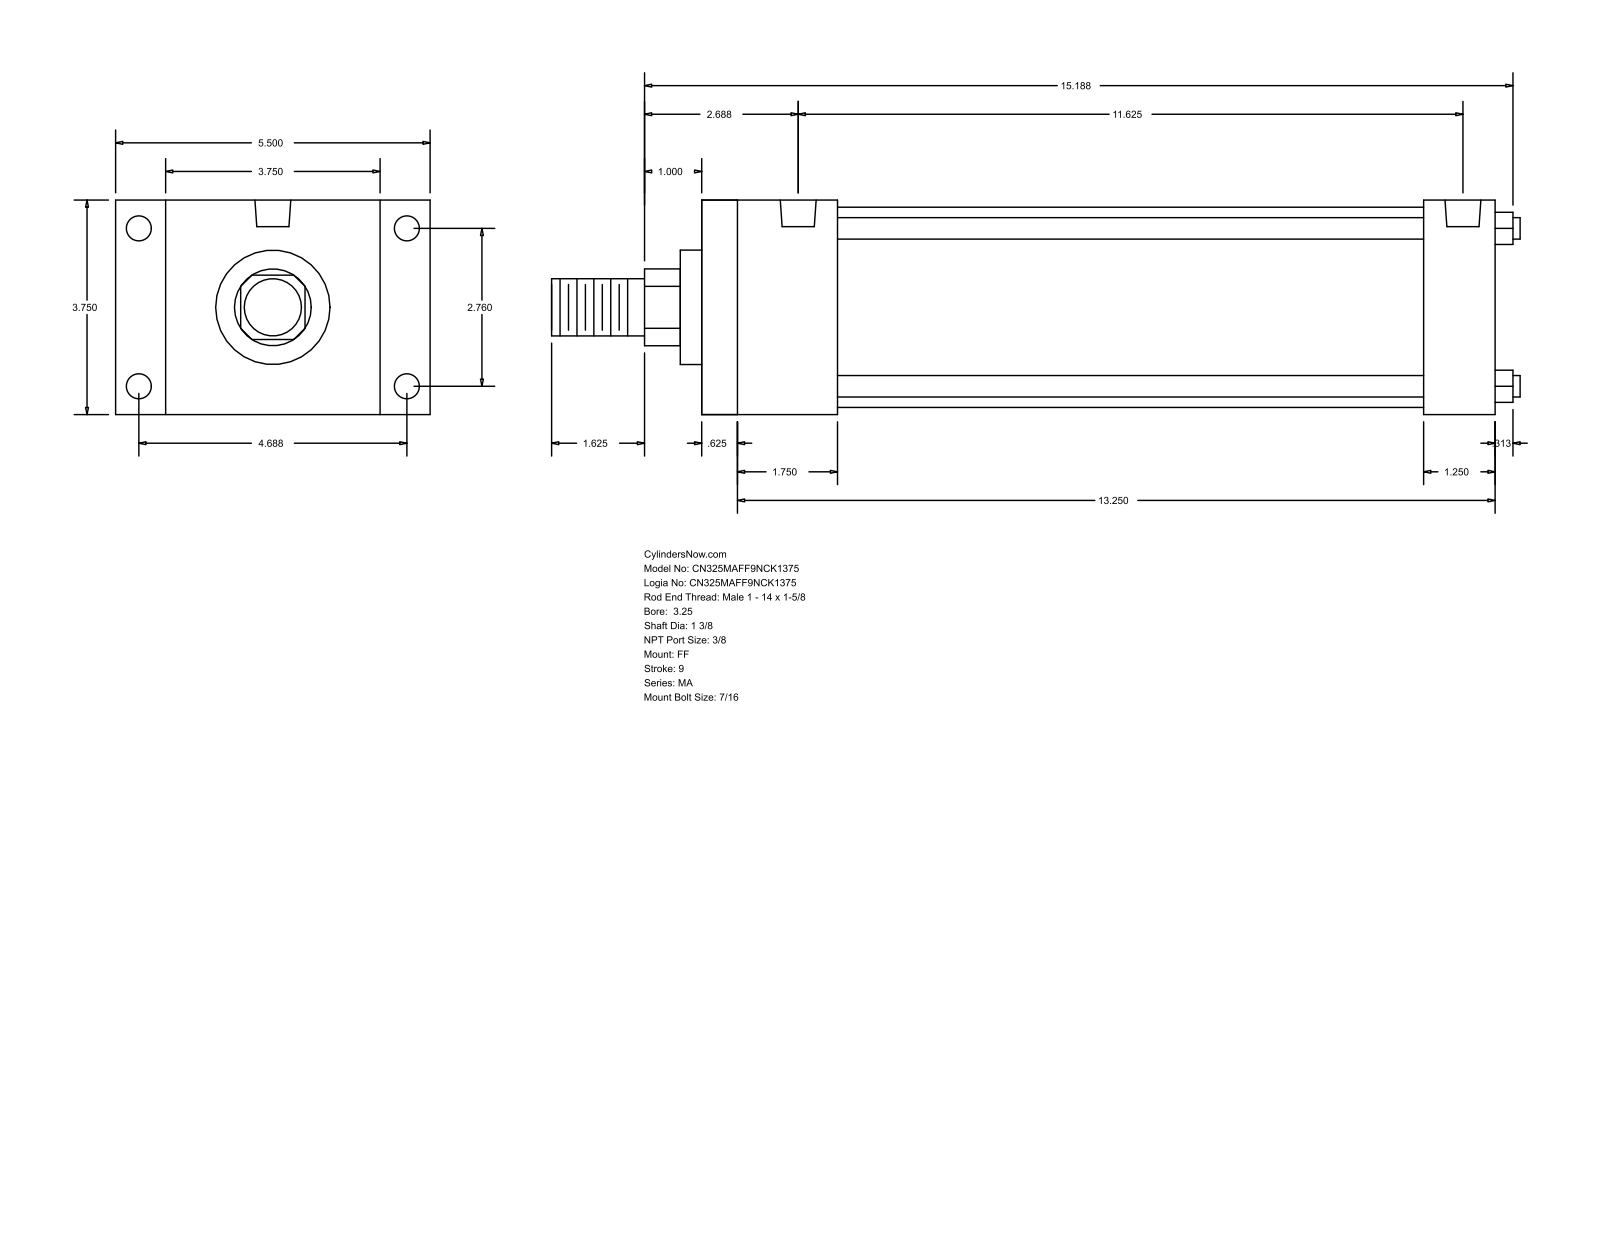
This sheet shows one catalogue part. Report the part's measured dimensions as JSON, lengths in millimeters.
{"part_name": "MA_FF__0325_1.375", "step_written_by": "GSSL Pune (CONFIG_CONTROL_DESIGN)", "units": "millimeters", "bodies": {"solids": 0, "faces": 92, "planar": 64, "cylindrical": 28, "other": 0}, "overall_size": [430.21, 139.7, 95.25], "round_holes": [[11.11, 8], [15.93, 2]], "round_bosses_or_shafts": [[9.53, 4], [88.9, 1], [50.8, 1], [34.92, 1], [25.4, 1]], "partial_cylinders_radius": [[17.06, 1]], "face_to_face_distances": [95.24, 352.42, 15.87, 336.55, 22.23, 117.47, 60.32, 320.67, 44.45, 304.8], "hole_center_spacings": [4.77, 70.1, 119.06, 138.16, 285.74, 290.51, 295.28]}
